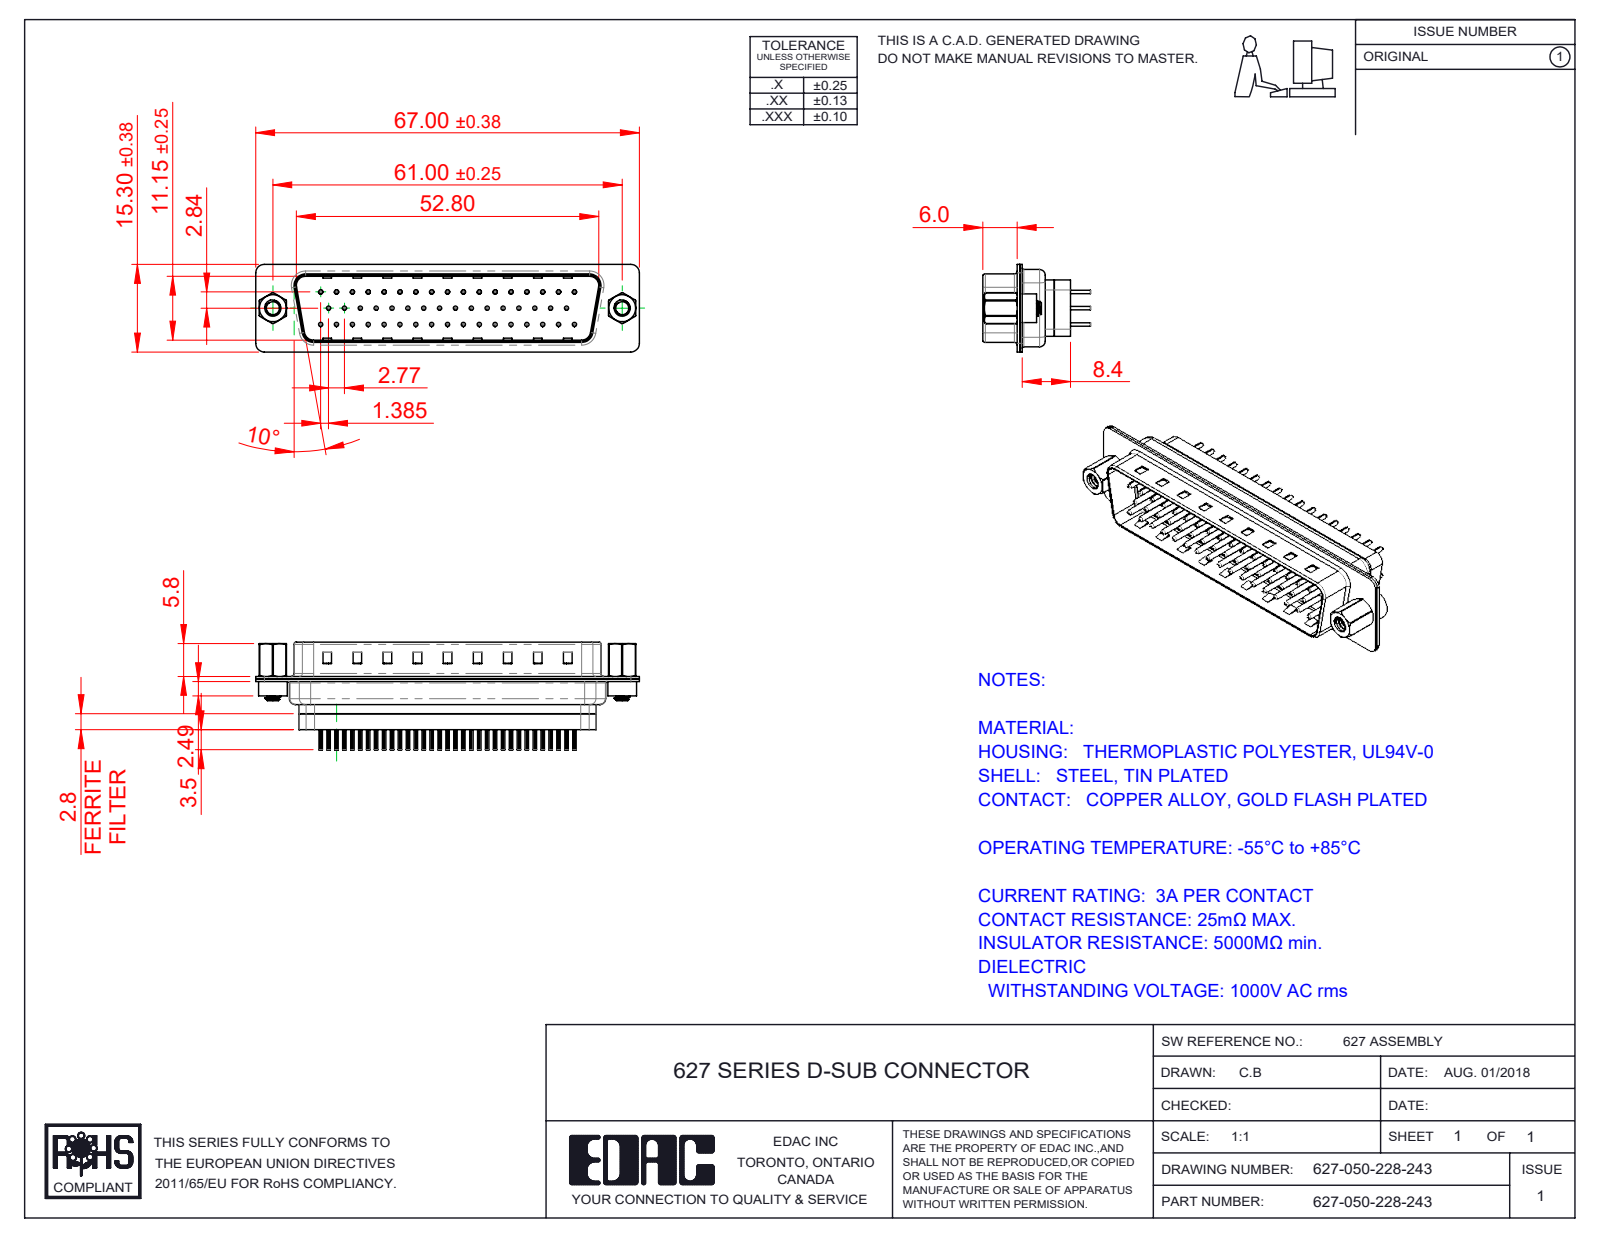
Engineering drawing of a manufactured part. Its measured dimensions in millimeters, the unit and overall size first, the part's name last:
Units: millimetres
Overall size (bounding box): 67 × 18.8 × 15.3
Round holes (diameter × count): ⌀0.2 ×50, ⌀0.35 ×50, ⌀1.1 ×50, ⌀1.6 ×50, ⌀2.26 ×2, ⌀2.29 ×2, ⌀4 ×2, ⌀4.8 ×2
Round bosses / shafts (diameter × count): ⌀2 ×50, ⌀1.5 ×50, ⌀0.75 ×50, ⌀0.6 ×50, ⌀5 ×2, ⌀4.9 ×2, ⌀2.79 ×2
Partial cylindrical surfaces — rounded edges, fillets, slot ends (radius × count): R0.1 ×100, R1.5 ×16, R2 ×12, R0.5 ×8, R1.6 ×8, R0.25 ×4, R0.6 ×4, R0.65 ×4
Main face-to-face distances: 0.4, 6.05, 0.45, 11.55, 0.9, 2.8, 8.85, 6.5, 9.3, 0.78
Hole centre spacings: 2.77, 3.16, 5.54, 8.31, 11.08, 13.85, 16.62, 19.39
Volume: 5 762 mm³ · Surface area: 15 103 mm²
Bodies: 58 solids, 5545 faces (1431 planar, 2166 cylindrical, 1948 other)
Part name (STEP PRODUCT): 627 Housing_50 FF; 627 Shell Rear_50 Contacts; 627 Contact Row 1_28L; 627-050-228-043 (+5 more)
STEP written by: SolidWorks 2020 (CONFIG_CONTROL_DESIGN)
